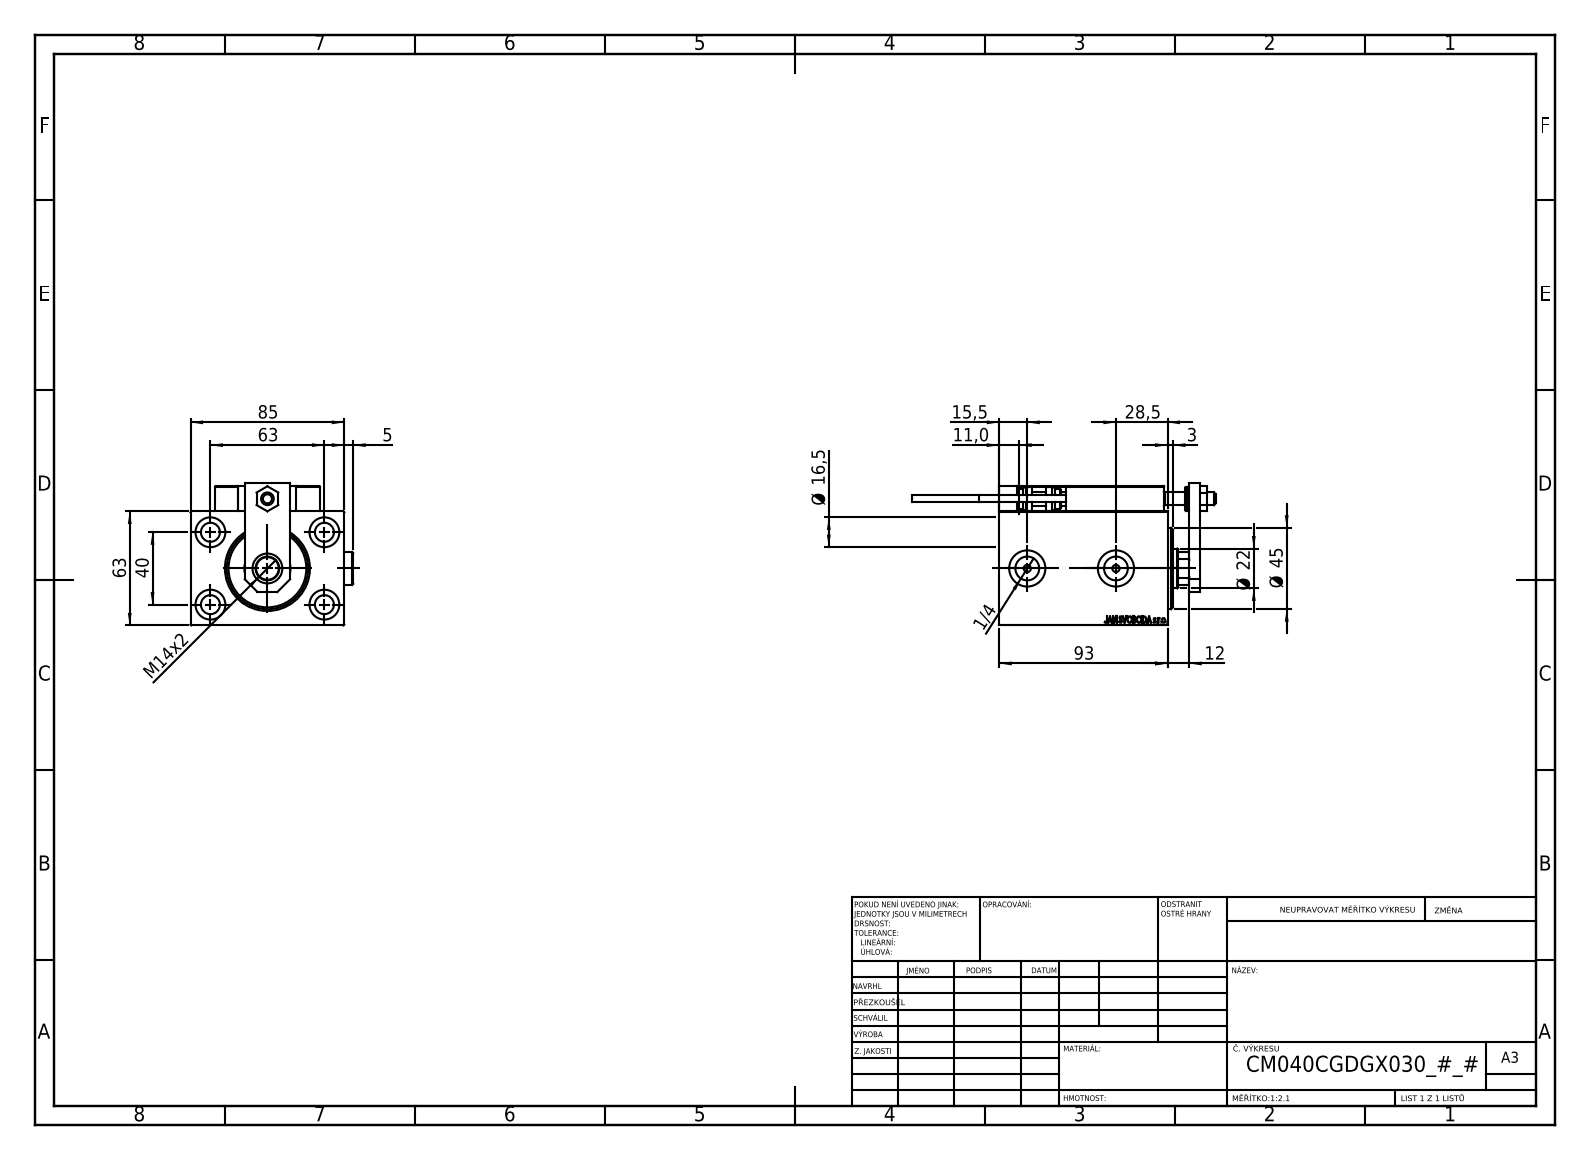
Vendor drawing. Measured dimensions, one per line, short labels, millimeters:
name: SWITCH_X_FRONT_BACK; Zatka_OIL_PORT; V450CM_C_VCP; ALLEN BOLT D8 (+7 more)
written by: SolidWorks 2019 (CONFIG_CONTROL_DESIGN)
unit: mm
bodies: 25 solids, 1336 faces (594 planar, 204 cylindrical, 538 other)
size: 167.7 × 89.9 × 78.5
volume: 476 745 mm³; area: 108 029 mm²
holes: 6× ⌀4, 5× ⌀8, 5× ⌀16.5, 4× ⌀3.2, 4× ⌀10.5, 2× ⌀5, 2× ⌀13.16, 2× ⌀20, 1× ⌀7, 1× ⌀12.5, 1× ⌀22, 1× ⌀25.5
bosses: 2× ⌀18, 2× ⌀5, 2× ⌀3.8, 1× ⌀13, 1× ⌀11
rounds: 30× R0.3, 2× R3, 1× R10.5
face distances: 63, 12, 85, 81, 93, 14, 30, 77, 45, 15
hole spacings: 37.31, 11.37, 20, 29.59, 29.69, 36.06, 36.53, 40
